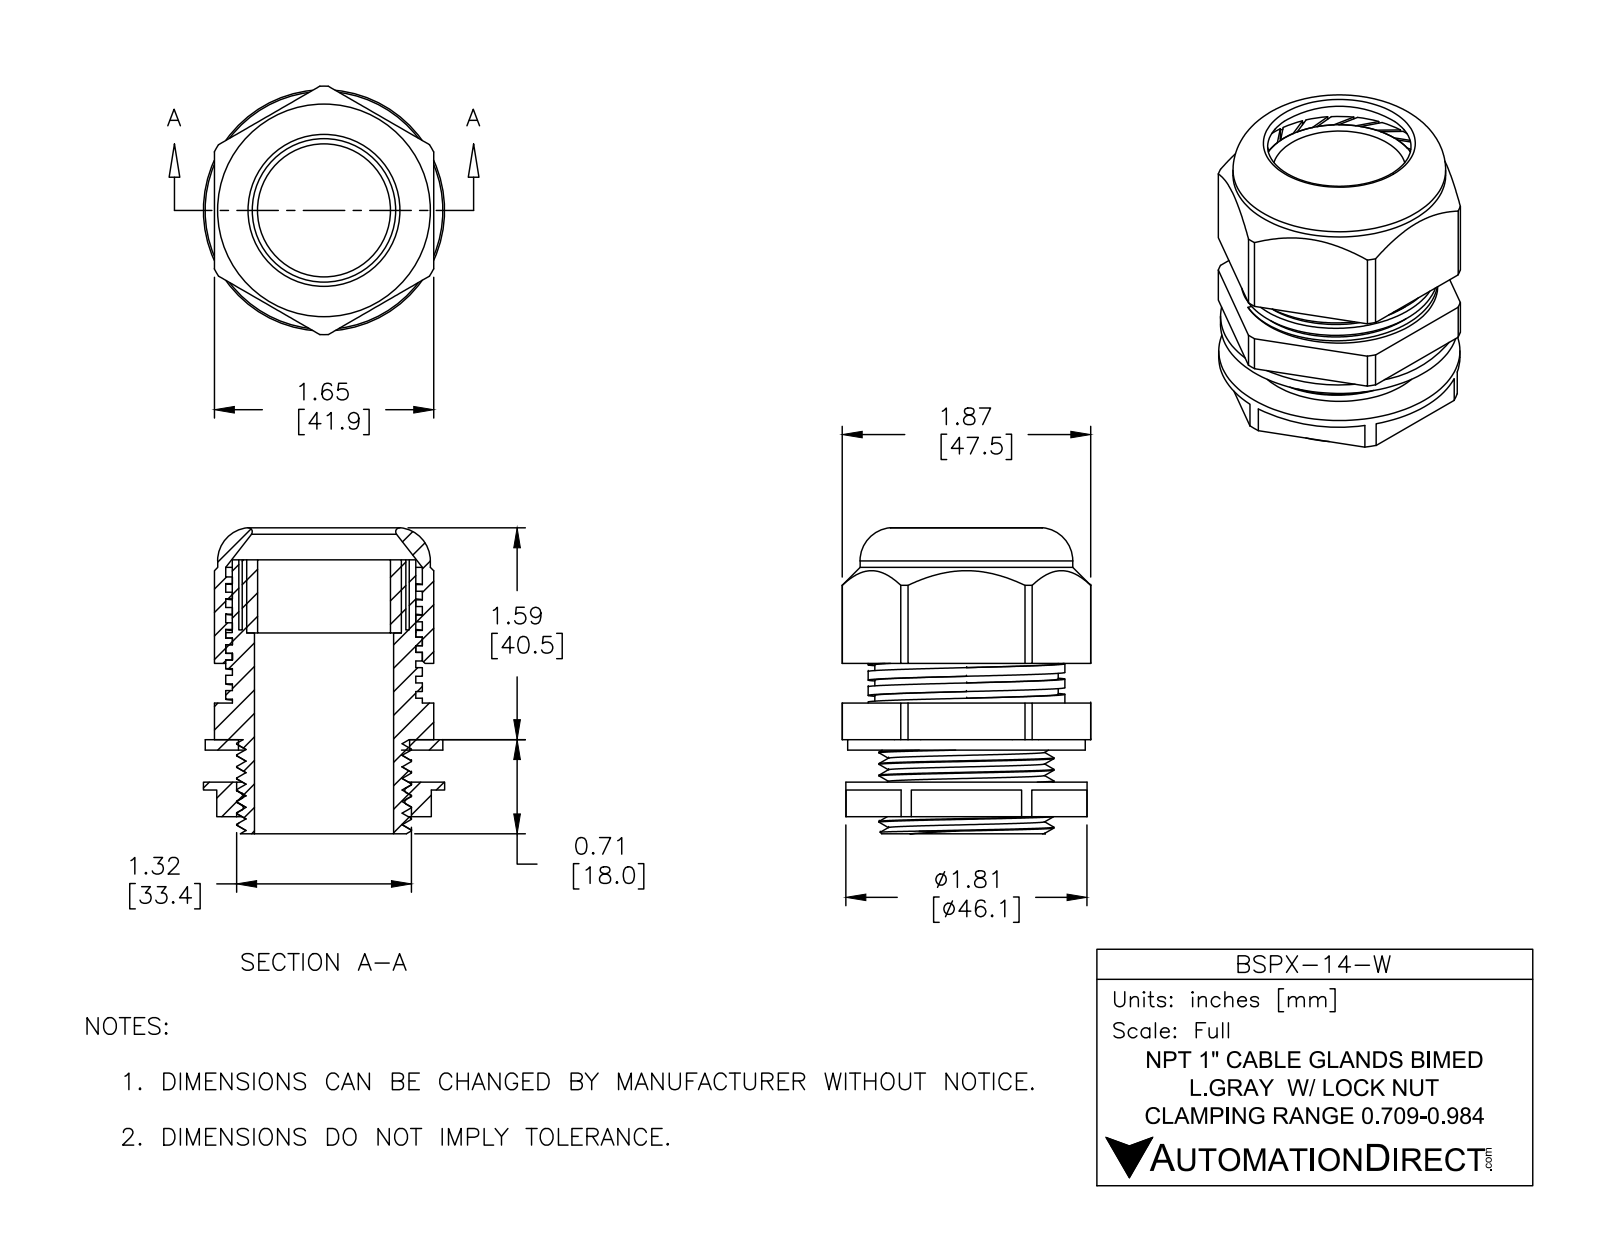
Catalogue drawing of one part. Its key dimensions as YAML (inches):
part_name: "BSPX-14-W"
step_written_by: "SolidWorks 2015 (CONFIG_CONTROL_DESIGN)"
units: inches
bodies: {solids: 5, faces: 237, planar: 133, cylindrical: 78, other: 26}
overall_size: [2.301, 1.87, 1.815]
volume: 2.459
surface_area: 53.61
round_holes:
  - {diameter: 1, count: 1}
  - {diameter: 1.047, count: 1}
  - {diameter: 1.164, count: 1}
  - {diameter: 1.288, count: 1}
  - {diameter: 1.48, count: 1}
round_bosses_or_shafts:
  - {diameter: 1.815, count: 1}
  - {diameter: 1.788, count: 1}
  - {diameter: 1.6, count: 1}
  - {diameter: 1.381, count: 1}
  - {diameter: 1.315, count: 1}
partial_cylinders:
  - {radius: 0.02, count: 1}
  - {radius: 0.935, count: 1}
face_to_face_distances: [1.65, 0.02, 0.988, 0.319, 0.24, 0.079, 0.018, 1.632, 1.008, 0.26]
